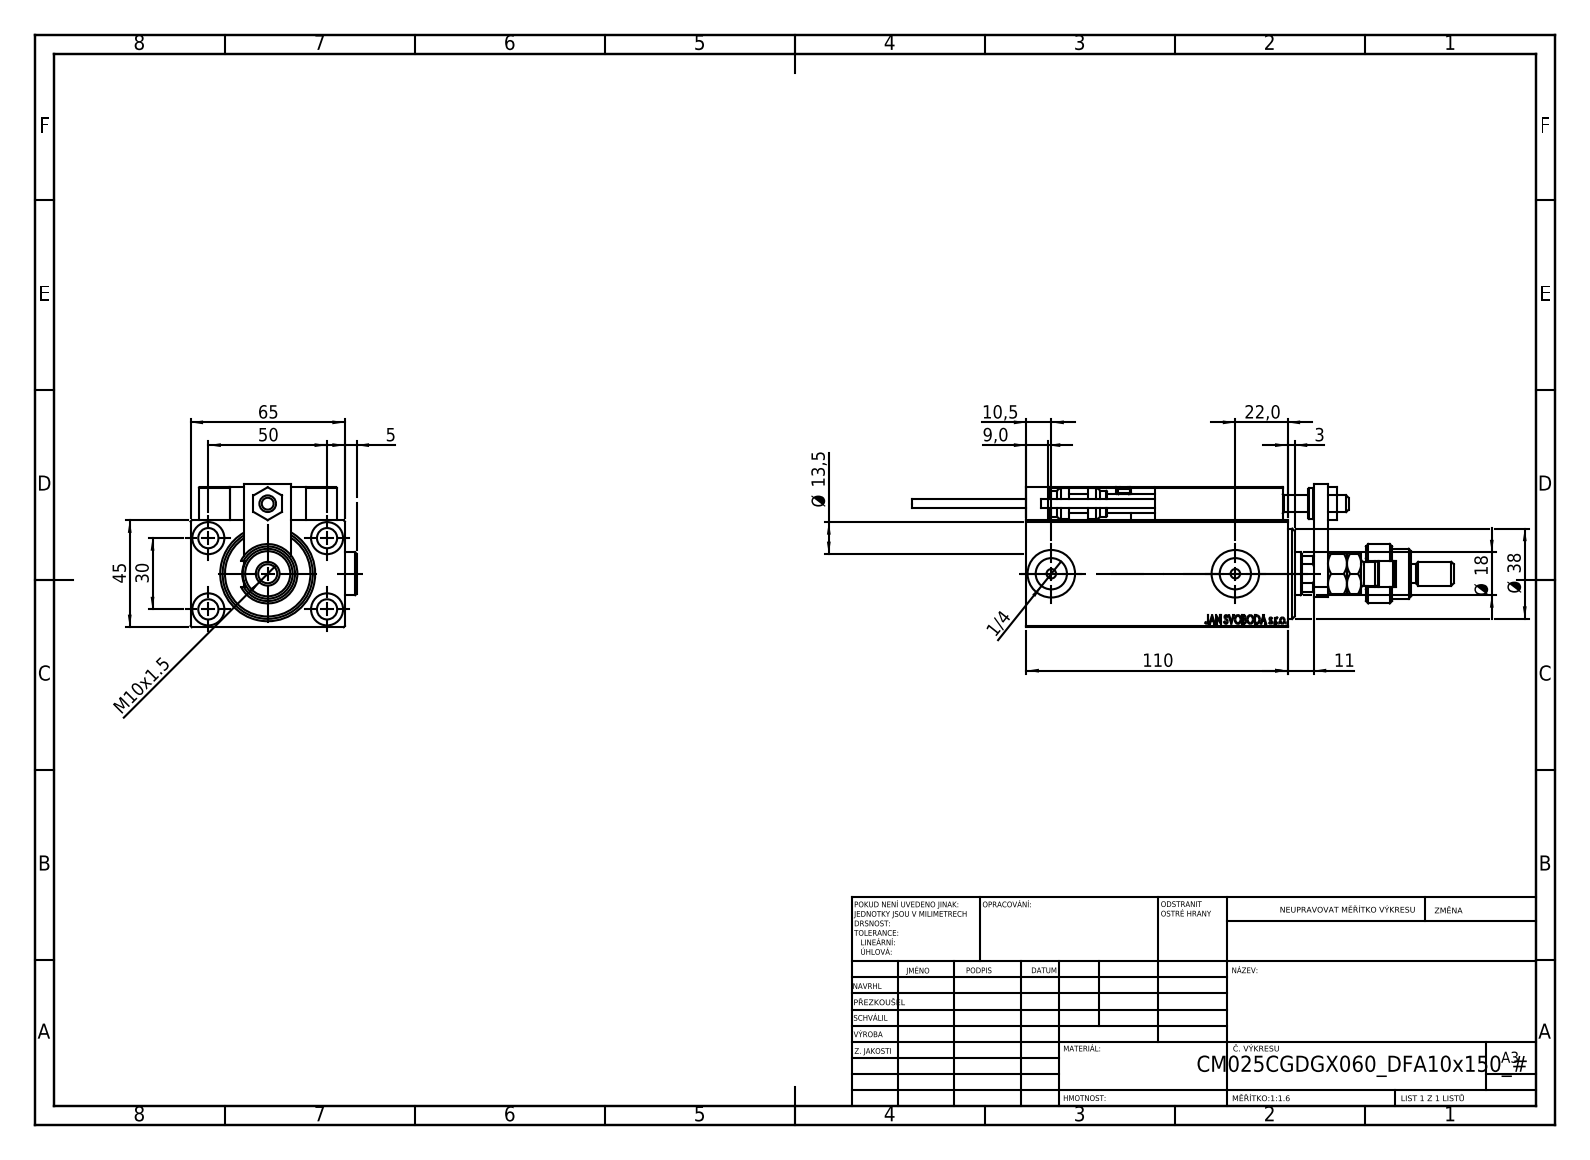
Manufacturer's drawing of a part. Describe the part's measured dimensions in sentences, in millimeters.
The part is named "TYC_L79; MFA; FEMALE_PART_FOR_DFA; Block (+7 more)". Its 3-D file was written by "SolidWorks 2019 (CONFIG_CONTROL_DESIGN)". It is 27 solids with 1421 faces: 622 planar, 217 cylindrical and 582 other. Overall it measures 228 by 69.9 by 60.5 millimeters. Its volume is 333 885 cubic millimeters and its surface area 96 955 square millimeters. Round holes: 6 of diameter 4, 5 of diameter 8, 5 of diameter 8.5, 4 of diameter 3.2, 4 of diameter 13.5, 2 of diameter 5, 2 of diameter 13.16, 2 of diameter 20, 1 of diameter 7, 1 of diameter 14.5, 1 of diameter 18, 1 of diameter 21.5. Round bosses or shafts: 2 of diameter 18, 2 of diameter 5, 2 of diameter 3.8, 1 of diameter 25, 1 of diameter 21, 1 of diameter 16, 1 of diameter 13, 1 of diameter 11. Partial cylindrical surfaces (rounded edges, fillets, slot ends): 30 of radius 0.3, 2 of radius 3, 1 of radius 5.5, 1 of radius 8.5, 1 of radius 8.75. The main face-to-face distances are 45, 65, 14, 6, 59, 3, 5, 7, 13, 121. The hole center spacings are 29.15, 11.37, 20, 28.9, 29.59, 29.69, 30, 36.06.
